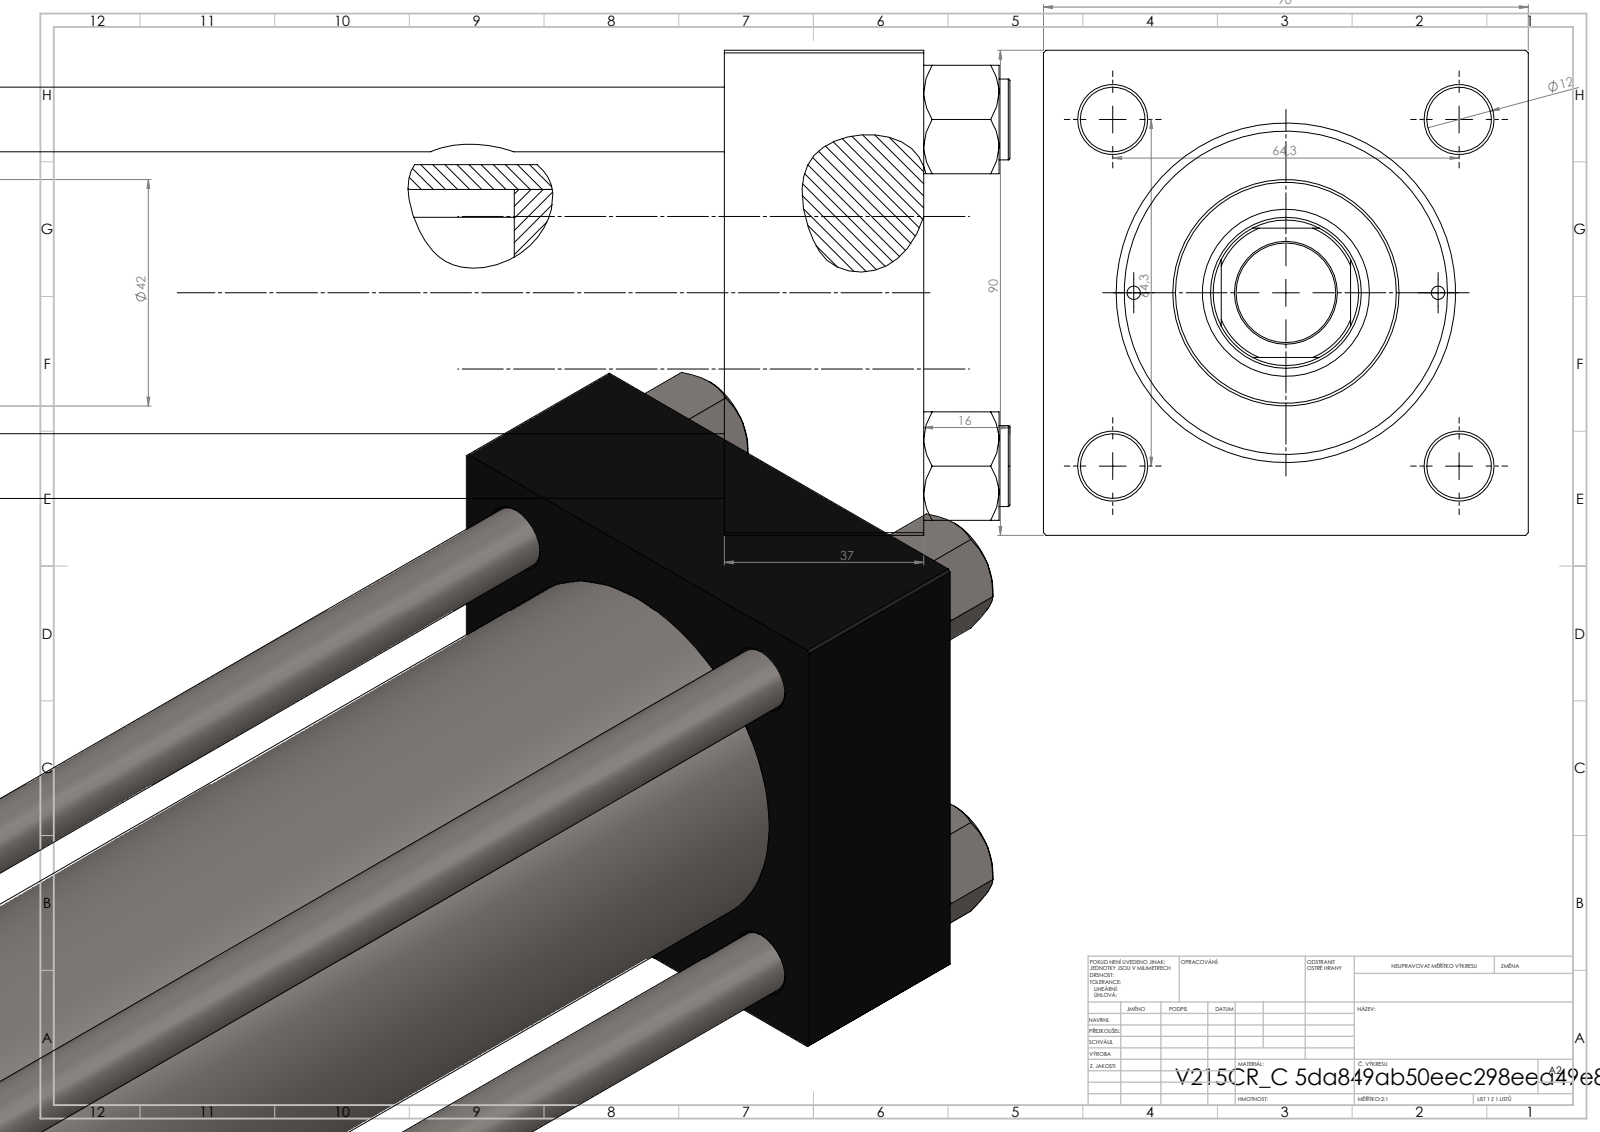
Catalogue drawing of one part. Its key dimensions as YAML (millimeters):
part_name: "V215CR_VCP_C; NUT_M5_C; V215CR_C_Body; V215CR_C_TYCINKA (+1 more)"
step_written_by: "SolidWorks 2019 (CONFIG_CONTROL_DESIGN)"
units: millimeters
bodies: {solids: 11, faces: 1154, planar: 528, cylindrical: 90, other: 536}
overall_size: [383, 90, 90]
volume: 1251000
surface_area: 296828
round_holes:
  - {diameter: 12, count: 4}
  - {diameter: 2.5, count: 2}
  - {diameter: 7, count: 2}
  - {diameter: 20.96, count: 2}
  - {diameter: 30, count: 2}
  - {diameter: 18.5, count: 1}
  - {diameter: 28, count: 1}
  - {diameter: 31, count: 1}
  - {diameter: 50, count: 1}
  - {diameter: 60, count: 1}
  - {diameter: 63, count: 1}
round_bosses_or_shafts:
  - {diameter: 15, count: 4}
  - {diameter: 69, count: 1}
  - {diameter: 42, count: 1}
partial_cylinders:
  - {radius: 13.5, count: 1}
face_to_face_distances: [90, 37, 335, 298, 276, 239, 59, 306.3, 269.3, 30.3]
hole_center_spacings: [32.39, 45.47, 64.3, 68.42, 28.25, 90.93, 56.5, 277.5]
